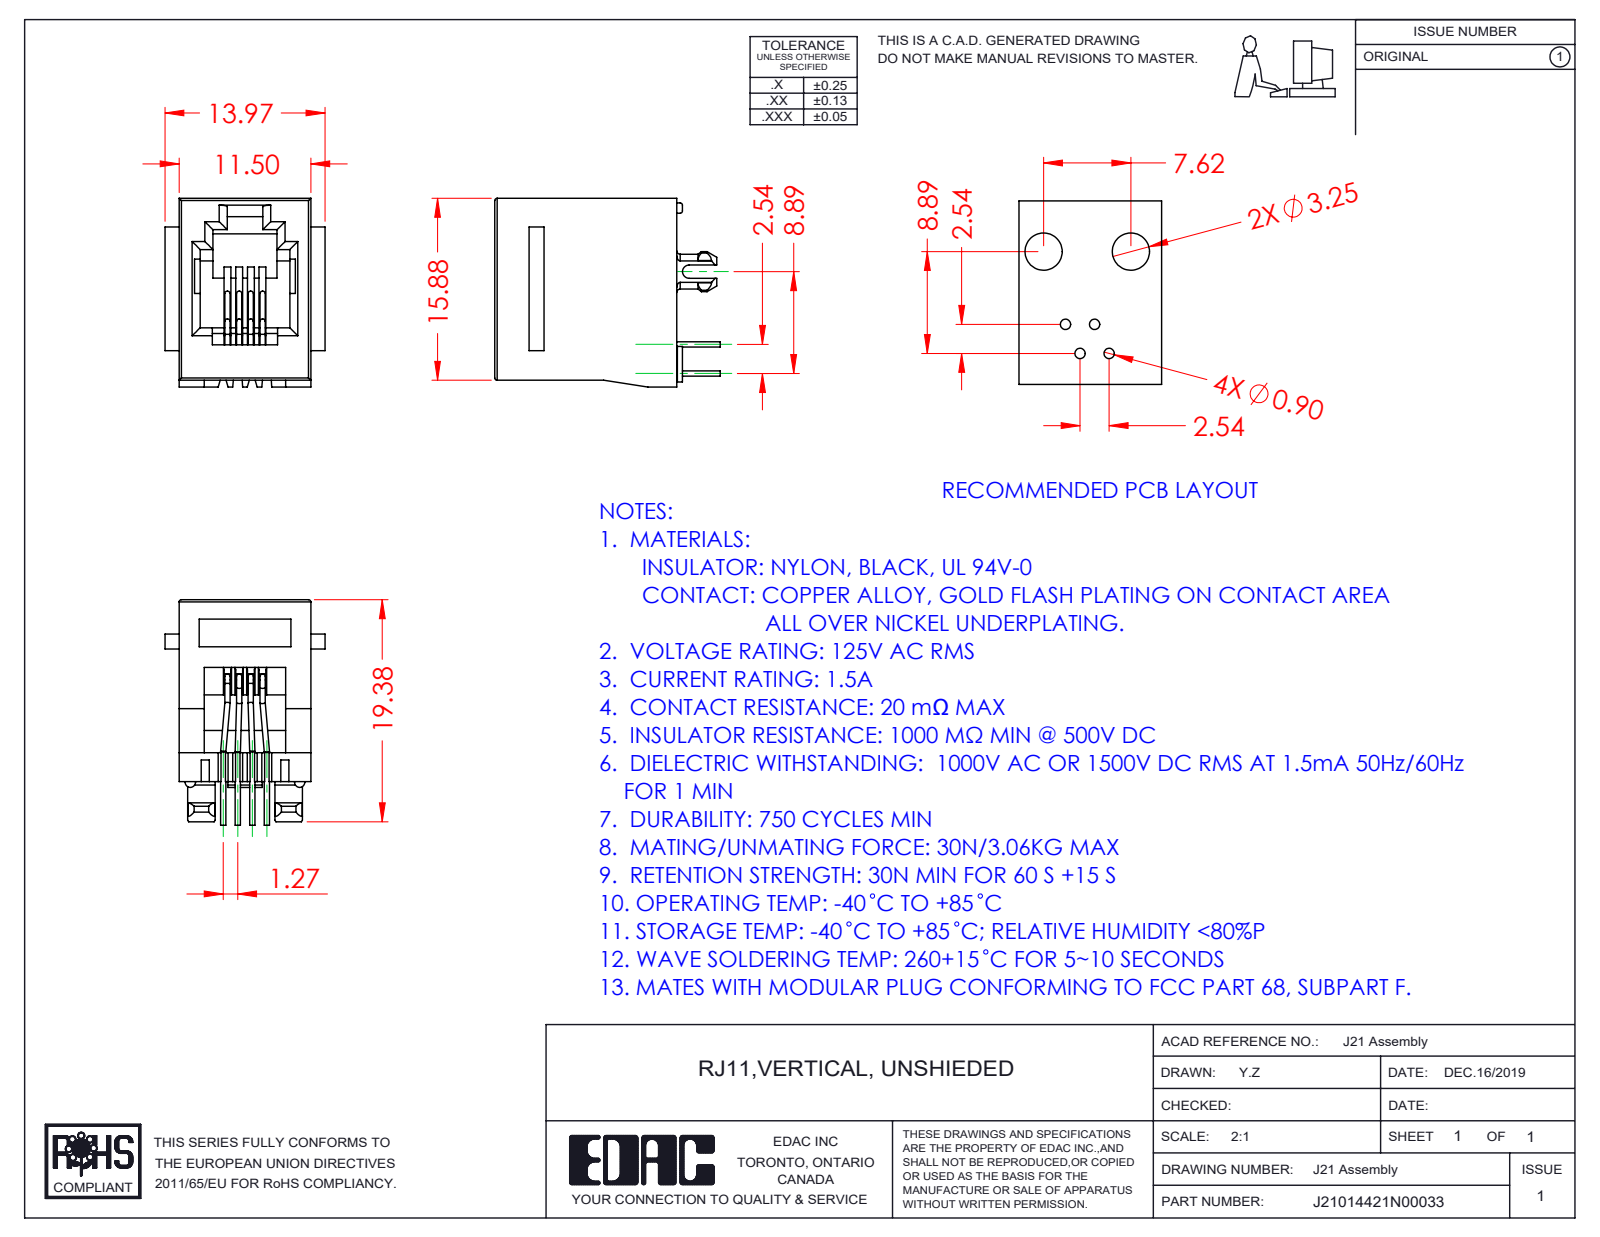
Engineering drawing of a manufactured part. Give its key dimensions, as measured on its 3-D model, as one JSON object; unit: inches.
{"part_name": "21 Contacts; RJ21014421N00033; 21 Insulator", "step_written_by": "SolidWorks 2016 (CONFIG_CONTROL_DESIGN)", "units": "inches", "bodies": {"solids": 5, "faces": 369, "planar": 230, "cylindrical": 111, "other": 28}, "overall_size": [0.775, 0.649, 0.55], "volume_in3": 0.099, "surface_area_in2": 3.974, "round_holes": [[0.079, 2]], "round_bosses_or_shafts": [[0.018, 24]], "partial_cylinders_radius": [[0.02, 9], [0.028, 9], [0.008, 7], [0.009, 4], [0.018, 2], [0.06, 2], [0.069, 2], [0.022, 1]], "face_to_face_distances": [0.453, 0.063, 0.625, 0.04, 0.283, 0.024, 0.116, 0.337, 0.08, 0.053], "hole_center_spacings": [0.331]}
